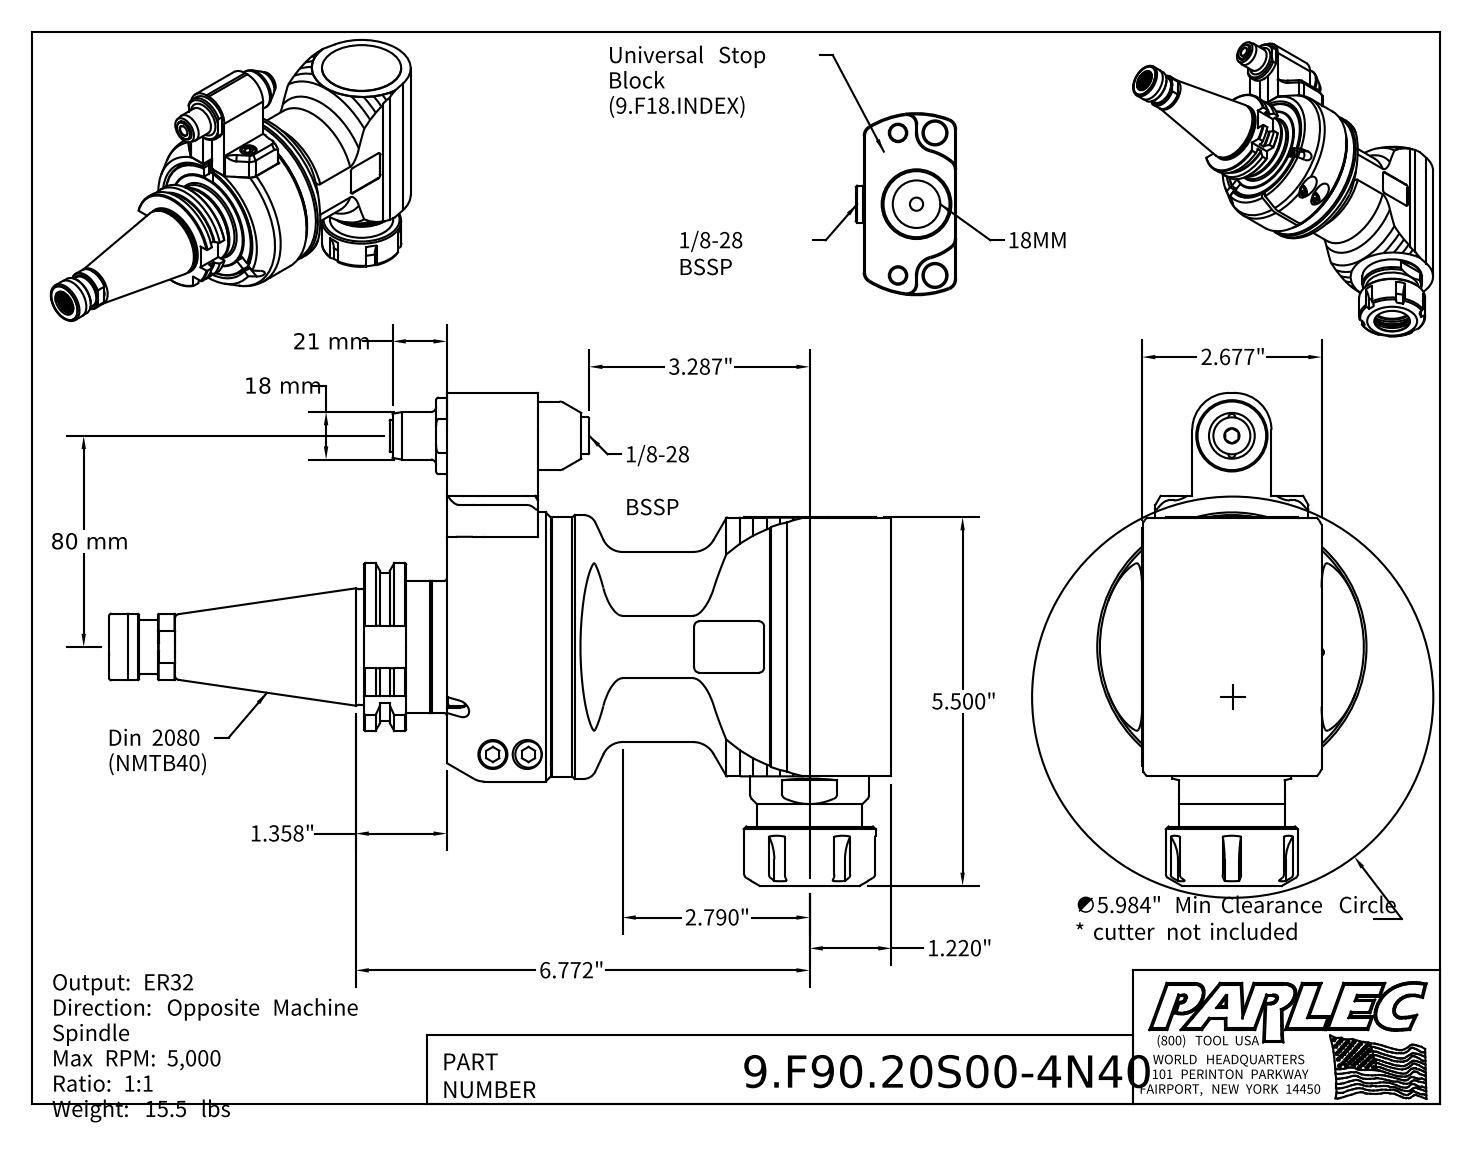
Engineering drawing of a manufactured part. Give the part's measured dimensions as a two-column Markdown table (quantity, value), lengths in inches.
| quantity | value |
| --- | --- |
| part name | 9.F90.20S00-4N40; 9_F90_20S00; 9_GA1_248_2 (Type1, NMTB40, 80mm) |
| STEP written by | Autodesk Inventor 2022 (AUTOMOTIVE_DESIGN) |
| units | inches |
| bodies | 9 solids, 650 faces (279 planar, 152 cylindrical, 219 other) |
| overall size | 11.669 × 7.352 × 4.016 |
| volume | 75.04 in³ |
| surface area | 269.9 in² |
| round holes (diameter × count) | 0.102 × 2, 0.165 × 2, 0.197 × 2, 0.276 × 2, 0.409 × 2, 0.433 × 2, 0.492 × 2, 1.063 × 2, 0.098 × 1, 0.118 × 1, 0.256 × 1, 0.472 × 1 |
| round bosses / shafts (diameter × count) | 0.394 × 4, 0.236 × 4, 1.969 × 2, 0.709 × 2, 0.098 × 2, 4.016 × 1, 3.937 × 1, 3.874 × 1 |
| partial cylindrical surfaces (radius × count) | 0.079 × 12, 0.591 × 6, 0.157 × 4, 0.02 × 2, 0.039 × 2, 0.138 × 2, 0.197 × 2, 0.236 × 2 |
| main face-to-face distances | 1.26, 0.02, 0.748, 0.285, 0.197, 1.555, 0.295, 1.28, 0.276, 0.335 |
| hole center spacings | 0.276, 0.512, 0.551, 1.72, 2.874, 3.15, 3.425, 4.138 |
